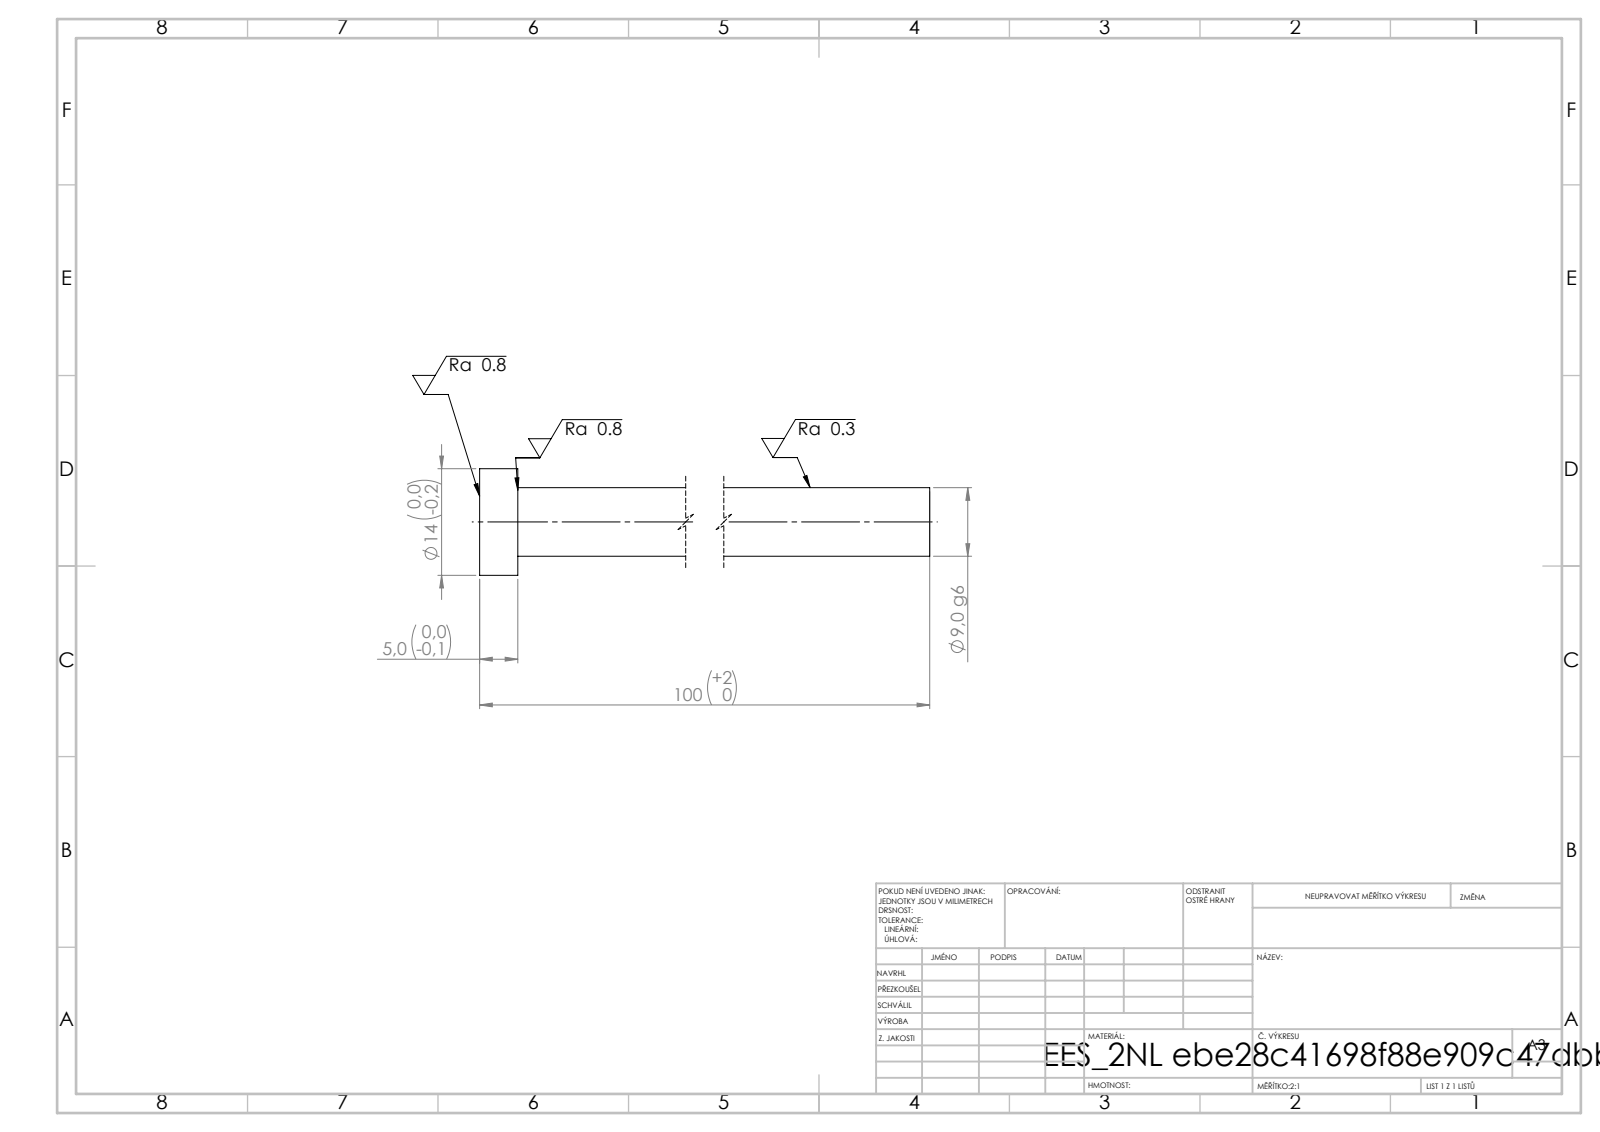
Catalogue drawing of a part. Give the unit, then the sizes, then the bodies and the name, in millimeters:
Units: millimetres
Overall size (bounding box): 100 × 14 × 14
Round bosses / shafts (diameter × count): ⌀14 ×1, ⌀9 ×1
Main face-to-face distances: 5, 100, 95
Volume: 6 813 mm³ · Surface area: 3 214 mm²
Bodies: 1 solid, 7 faces (3 planar, 4 cylindrical, 0 other)
STEP written by: SolidWorks 2019 (CONFIG_CONTROL_DESIGN)
